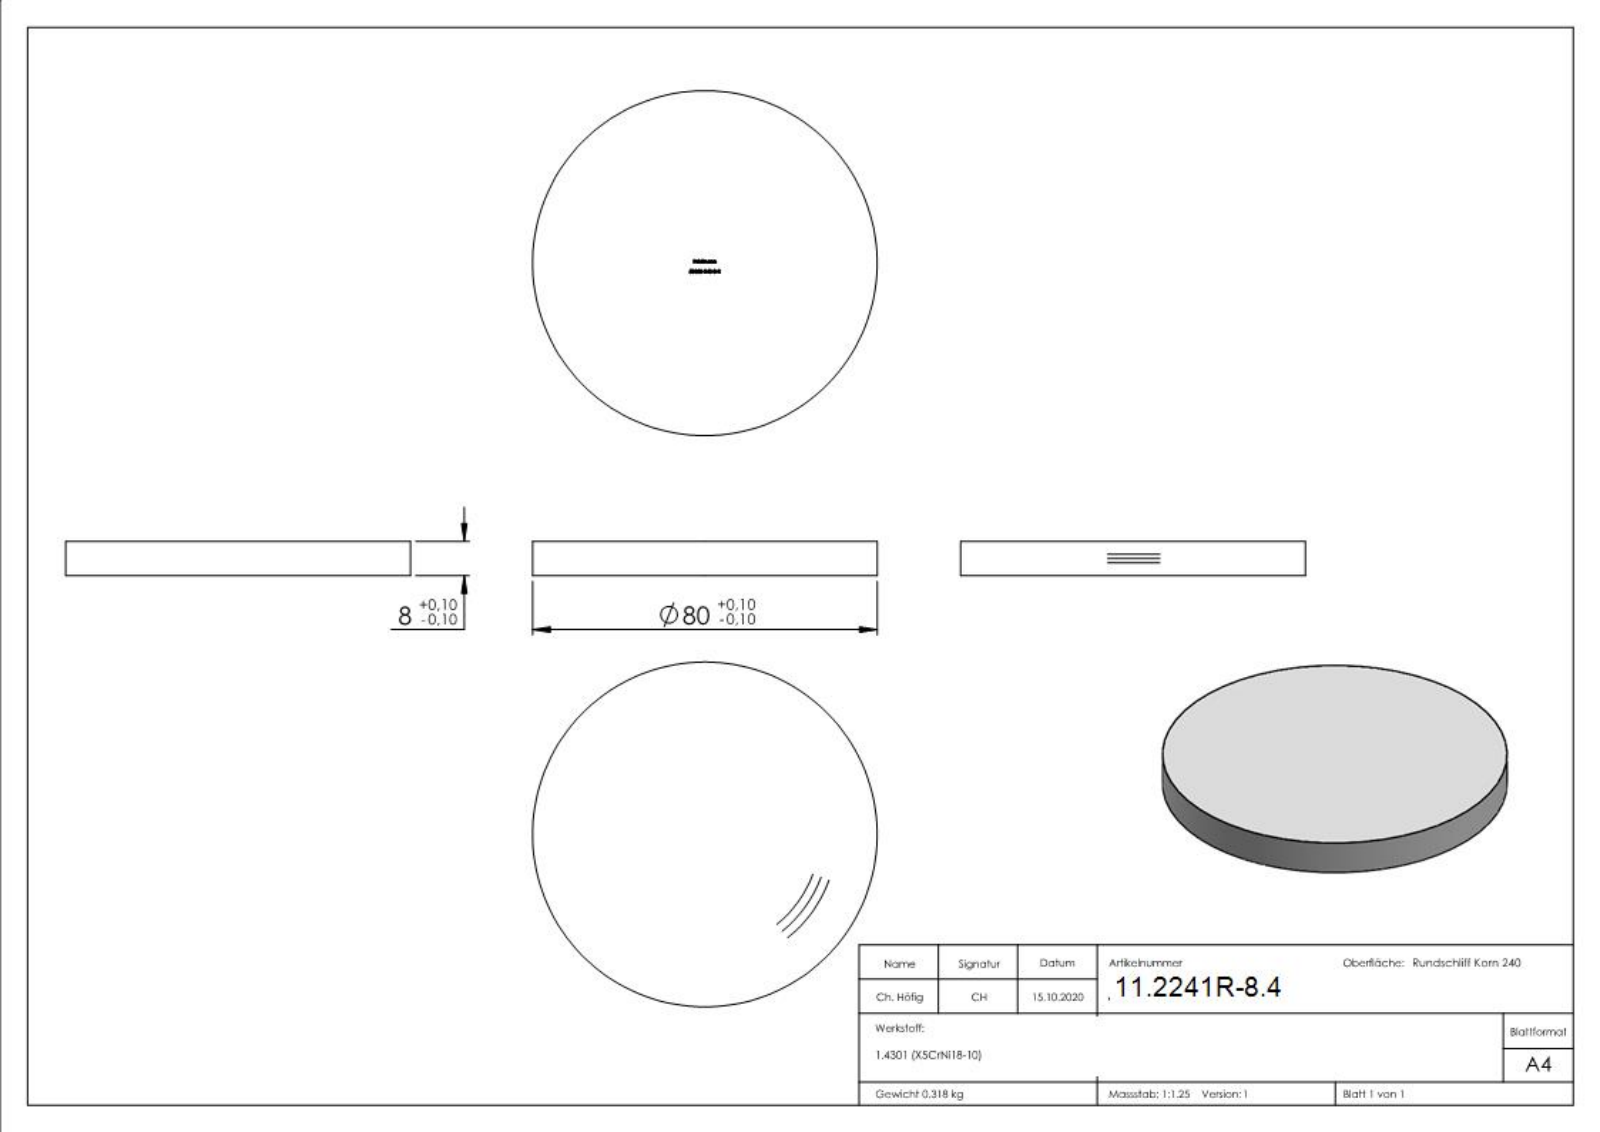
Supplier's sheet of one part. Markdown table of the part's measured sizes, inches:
| quantity | value |
| --- | --- |
| part name | 53080-240-8-R |
| STEP written by | SolidWorks 2018 (CONFIG_CONTROL_DESIGN) |
| units | inches |
| bodies | 1 solid, 284 faces (140 planar, 2 cylindrical, 142 other) |
| overall size | 3.15 × 3.15 × 0.315 |
| volume | 2.454 in³ |
| surface area | 18.71 in² |
| round bosses / shafts (diameter × count) | 3.15 × 1 |
| main face-to-face distances | 0.315, 0.311, 0.07, 0.096, 0.048, 0.174, 0.033, 0.109, 0.021, 0.039 |
